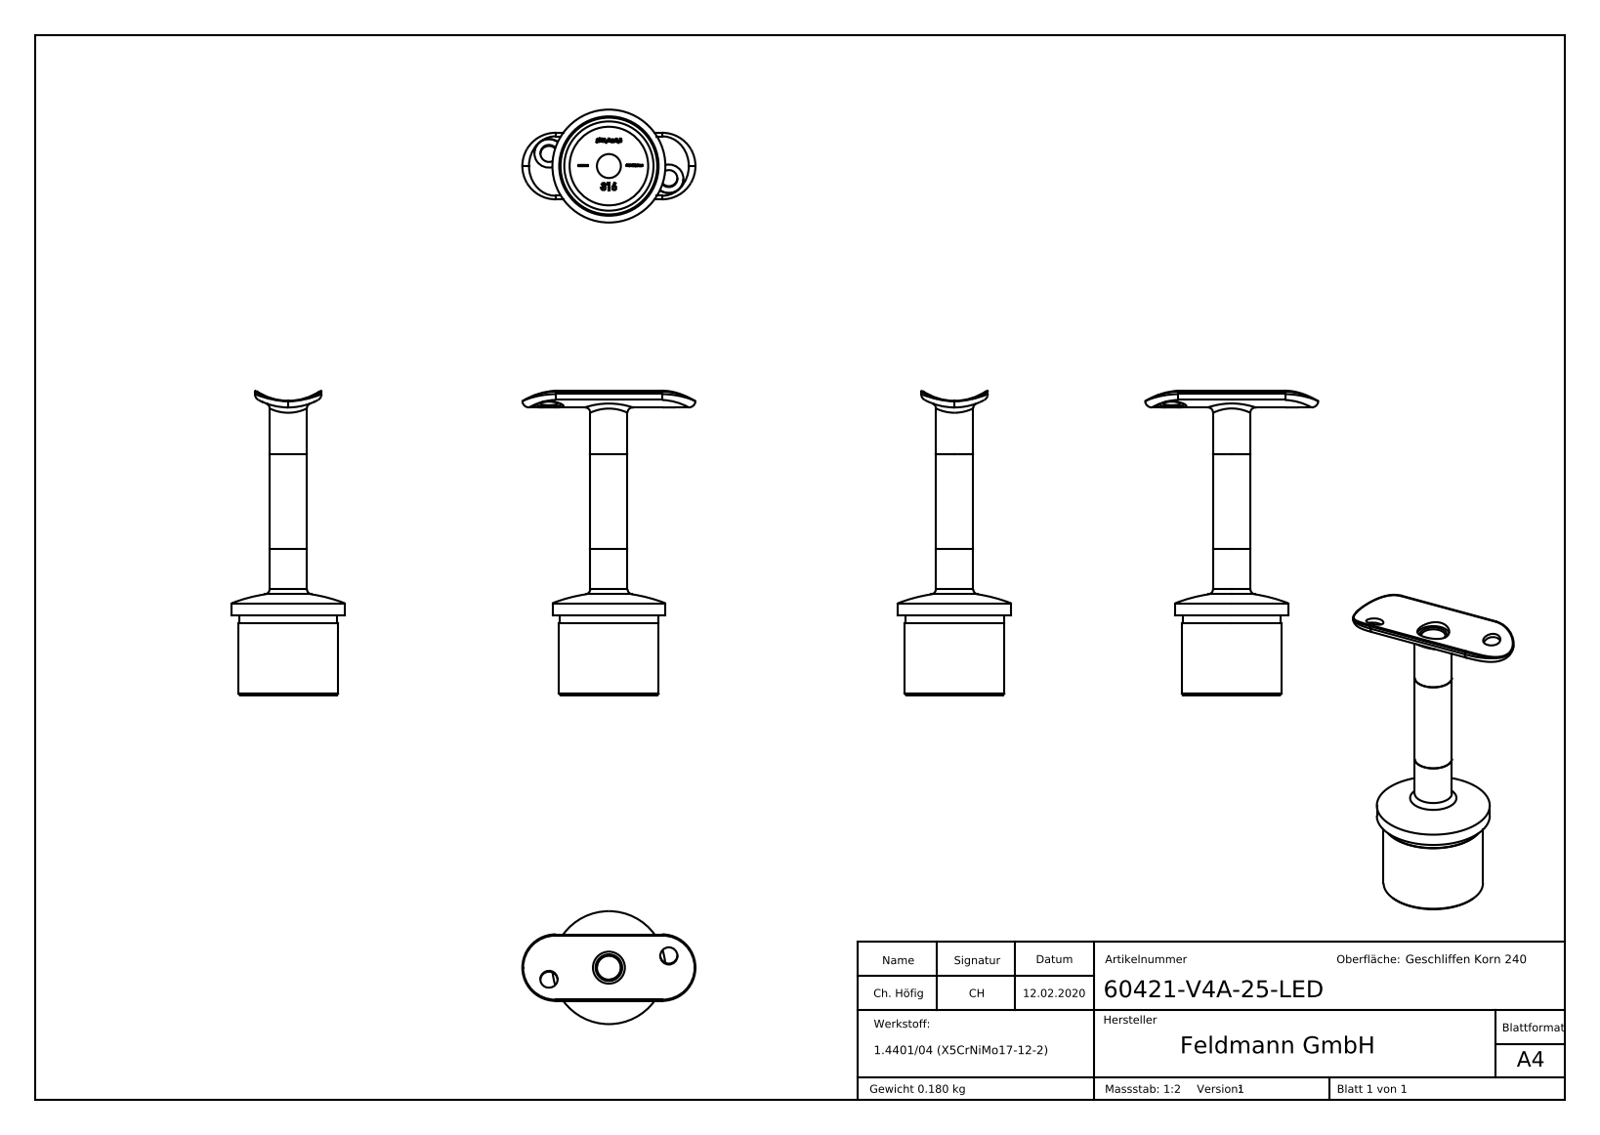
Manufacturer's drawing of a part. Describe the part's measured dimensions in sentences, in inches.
The part is named "604XX-XXX-LED Teil1_60421-V4A-25-LED Teil1; 604XX-XXX-LED Teil2; 604XX-XXX-LED Teil3_60421-V4A-25-LED Teil3; 604XX-XXX-LED Teil3 (+3 more)". Its 3-D file was written by "SolidWorks 2015 (CONFIG_CONTROL_DESIGN)". It is 3 solids with 511 faces: 317 planar, 29 cylindrical and 165 other. Overall it measures 4.5 by 2.558 by 1.669 inches. Its volume is 1.369 cubic inches and its surface area 30.03 square inches. Round holes: 2 of diameter 0.256, 2 of diameter 0.433, 1 of diameter 0.354, 1 of diameter 0.394, 1 of diameter 0.472, 1 of diameter 1.319. Round bosses or shafts: 1 of diameter 1.669, 1 of diameter 1.469, 1 of diameter 1.453, 1 of diameter 0.551, 1 of diameter 0.469. Partial cylindrical surfaces (rounded edges, fillets, slot ends): 2 of radius 0.012, 2 of radius 0.098, 2 of radius 0.492, 1 of radius 0.835, 1 of radius 0.933. The main face-to-face distances are 0.079, 1.181, 1.26, 0.984, 3.563, 2.382, 2.303, 2.165, 0.906, 1.398.
